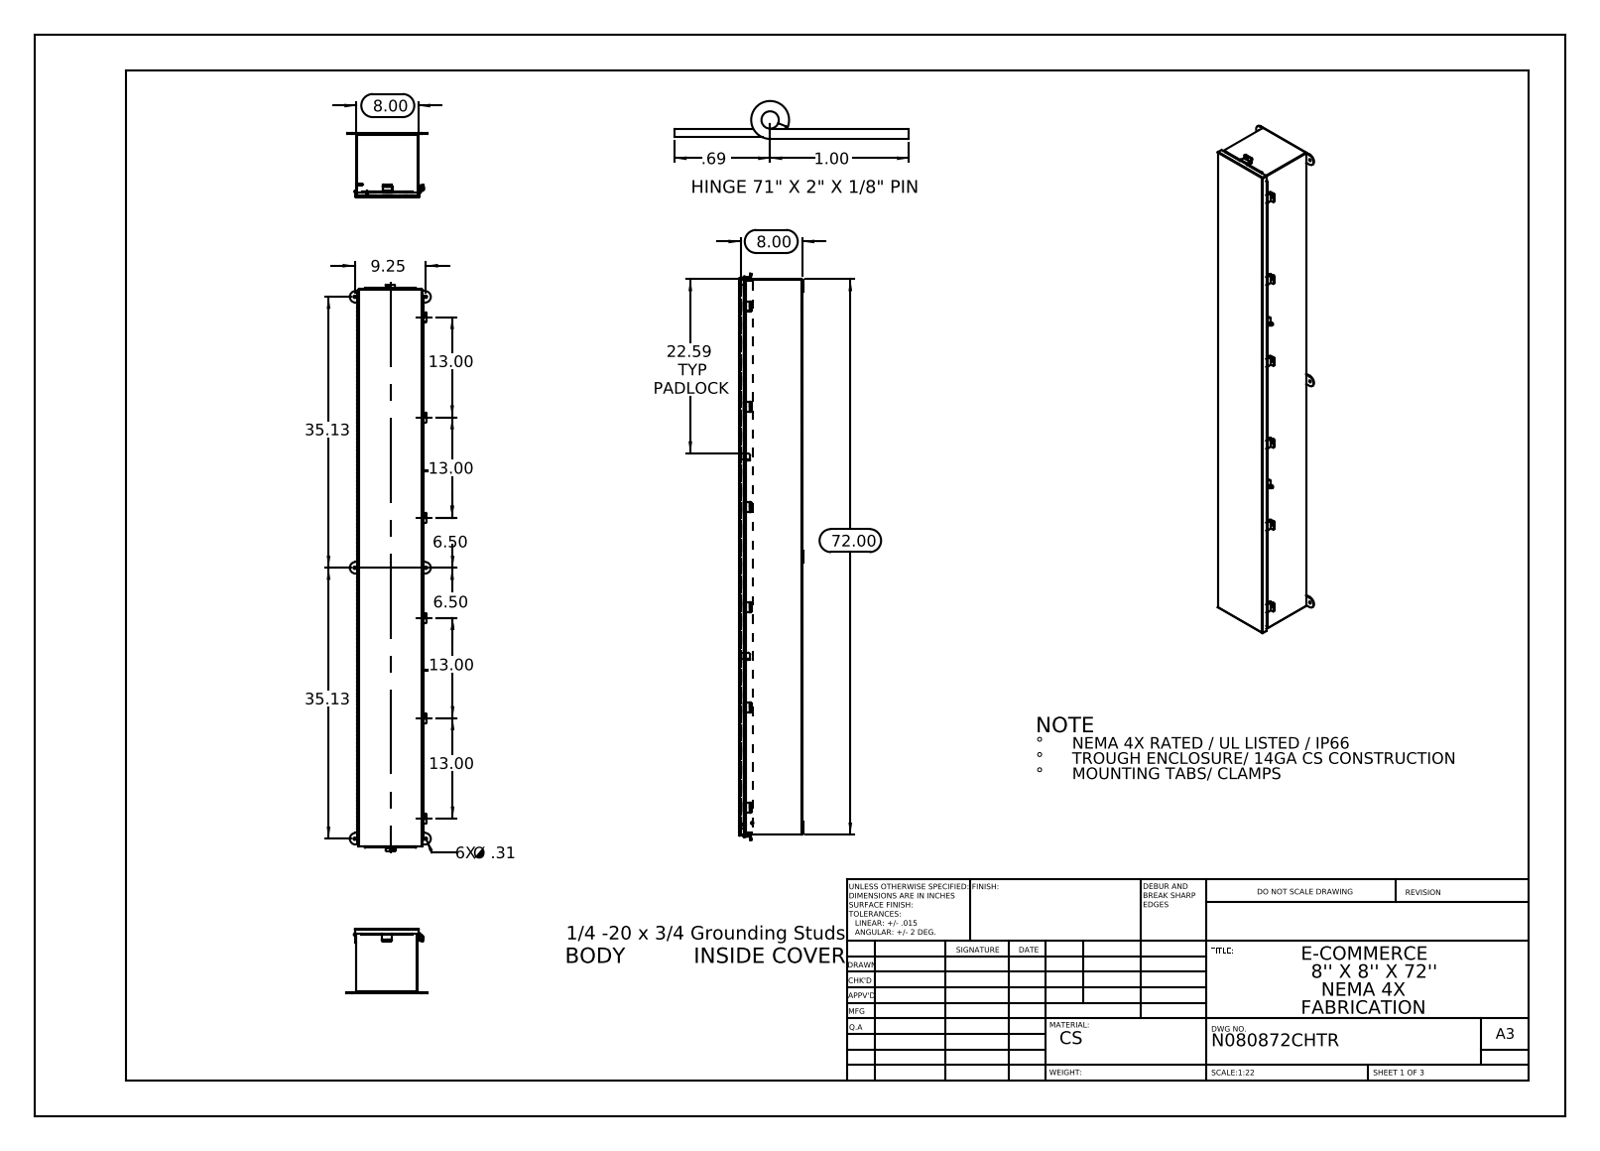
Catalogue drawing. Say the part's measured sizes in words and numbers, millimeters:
The part is named "N080872SSCHTR JIC Cover Clamp; N080872SSCHTR JIC Mounting Bracket; N080872SSCHTR Hinge Cover Side JIC; N080872SSCHTR JIC Bottom (+8 more)". Its 3-D file was written by "SolidWorks 2013 (CONFIG_CONTROL_DESIGN)". It is 29 solids with 1943 faces: 1154 planar, 769 cylindrical and 20 other. Overall it measures 1864.5 by 266.7 by 211.8 millimeters. Its volume is 3 471 000 cubic millimeters and its surface area 3 674 000 square millimeters. Round holes: 8 of diameter 6.4, 6 of diameter 8, 1 of diameter 3.2, 1 of diameter 3.2, 1 of diameter 9.5. Round bosses or shafts: 2 of diameter 8, 2 of diameter 6, 1 of diameter 6.9, 1 of diameter 6.4. Partial cylindrical surfaces (rounded edges, fillets, slot ends): 31 of radius 3.2, 16 of radius 3.4, 12 of radius 0.2, 10 of radius 0.3, 10 of radius 2.2, 6 of radius 2.1, 6 of radius 2.5, 6 of radius 19.1. The main face-to-face distances are 1.9, 201.3, 206.5, 203.2, 199.4, 208.4, 204.5, 3.8, 205.1, 1.9. The hole center spacings are 330.2, 660.4, 892.2, 922.6, 990.6, 235, 1320.8, 1784.4.
